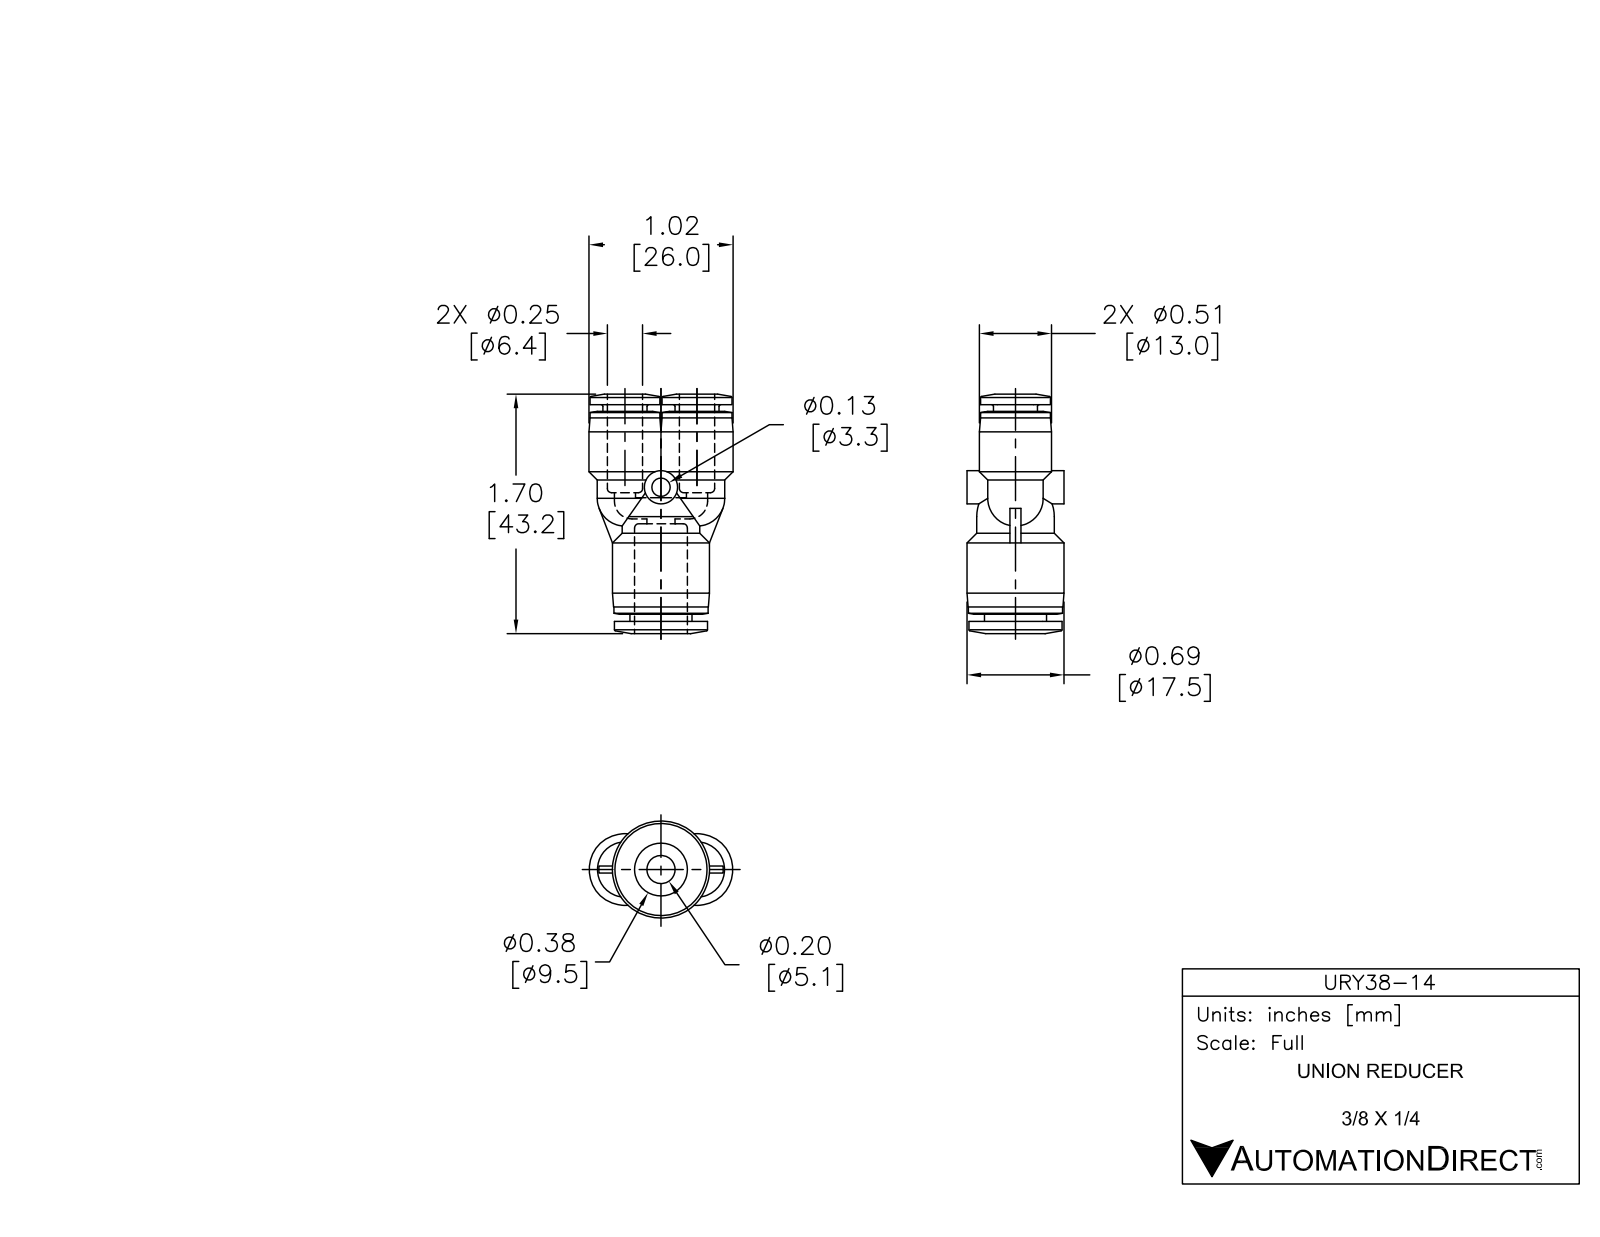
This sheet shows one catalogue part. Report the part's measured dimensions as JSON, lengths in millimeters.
{"part_name": "URY38-14", "step_written_by": "SolidWorks 2015 (AUTOMOTIVE_DESIGN)", "units": "millimeters", "bodies": {"solids": 1, "faces": 115, "planar": 19, "cylindrical": 41, "other": 55}, "overall_size": [43.2, 26, 17.5], "volume_mm3": 6780, "surface_area_mm2": 5482, "round_holes": [[6.6, 2], [3.3, 1], [9.8, 1]], "round_bosses_or_shafts": [[13, 2], [12.6, 2], [8, 2], [17.5, 1], [17, 1], [16.8, 1], [14, 1], [11.2, 1]], "partial_cylinders_radius": [[5, 2]], "face_to_face_distances": [39.1, 1.3, 37.8, 1.2, 37.9, 36.6, 17.6, 16.3, 20.3, 21.5], "hole_center_spacings": [6.5, 13]}
